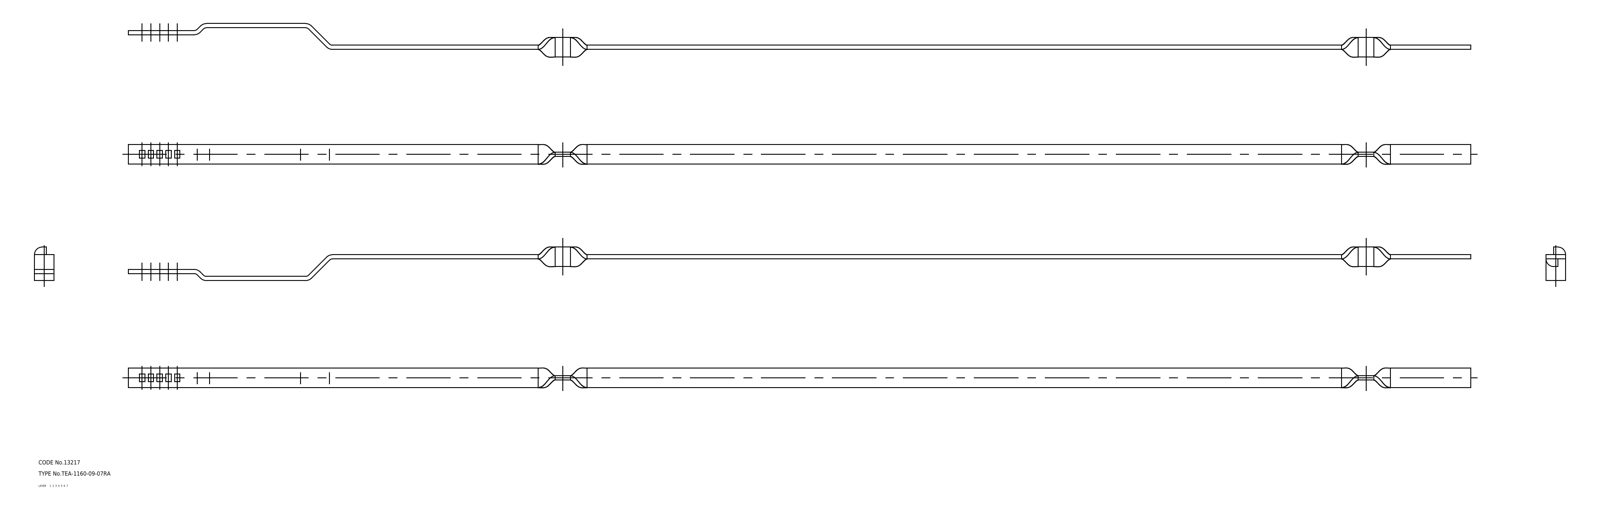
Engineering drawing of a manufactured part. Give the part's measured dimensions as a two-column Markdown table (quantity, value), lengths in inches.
| quantity | value |
| --- | --- |
| part name | rod |
| STEP written by | CADfix (AUTOMOTIVE_DESIGN) |
| units | inches |
| bodies | 1 solid, 74 faces (0 planar, 0 cylindrical, 74 other) |
| overall size | 37.835 × 0.946 × 0.572 |
| volume | 2.463 in³ |
| surface area | 51.54 in² |
